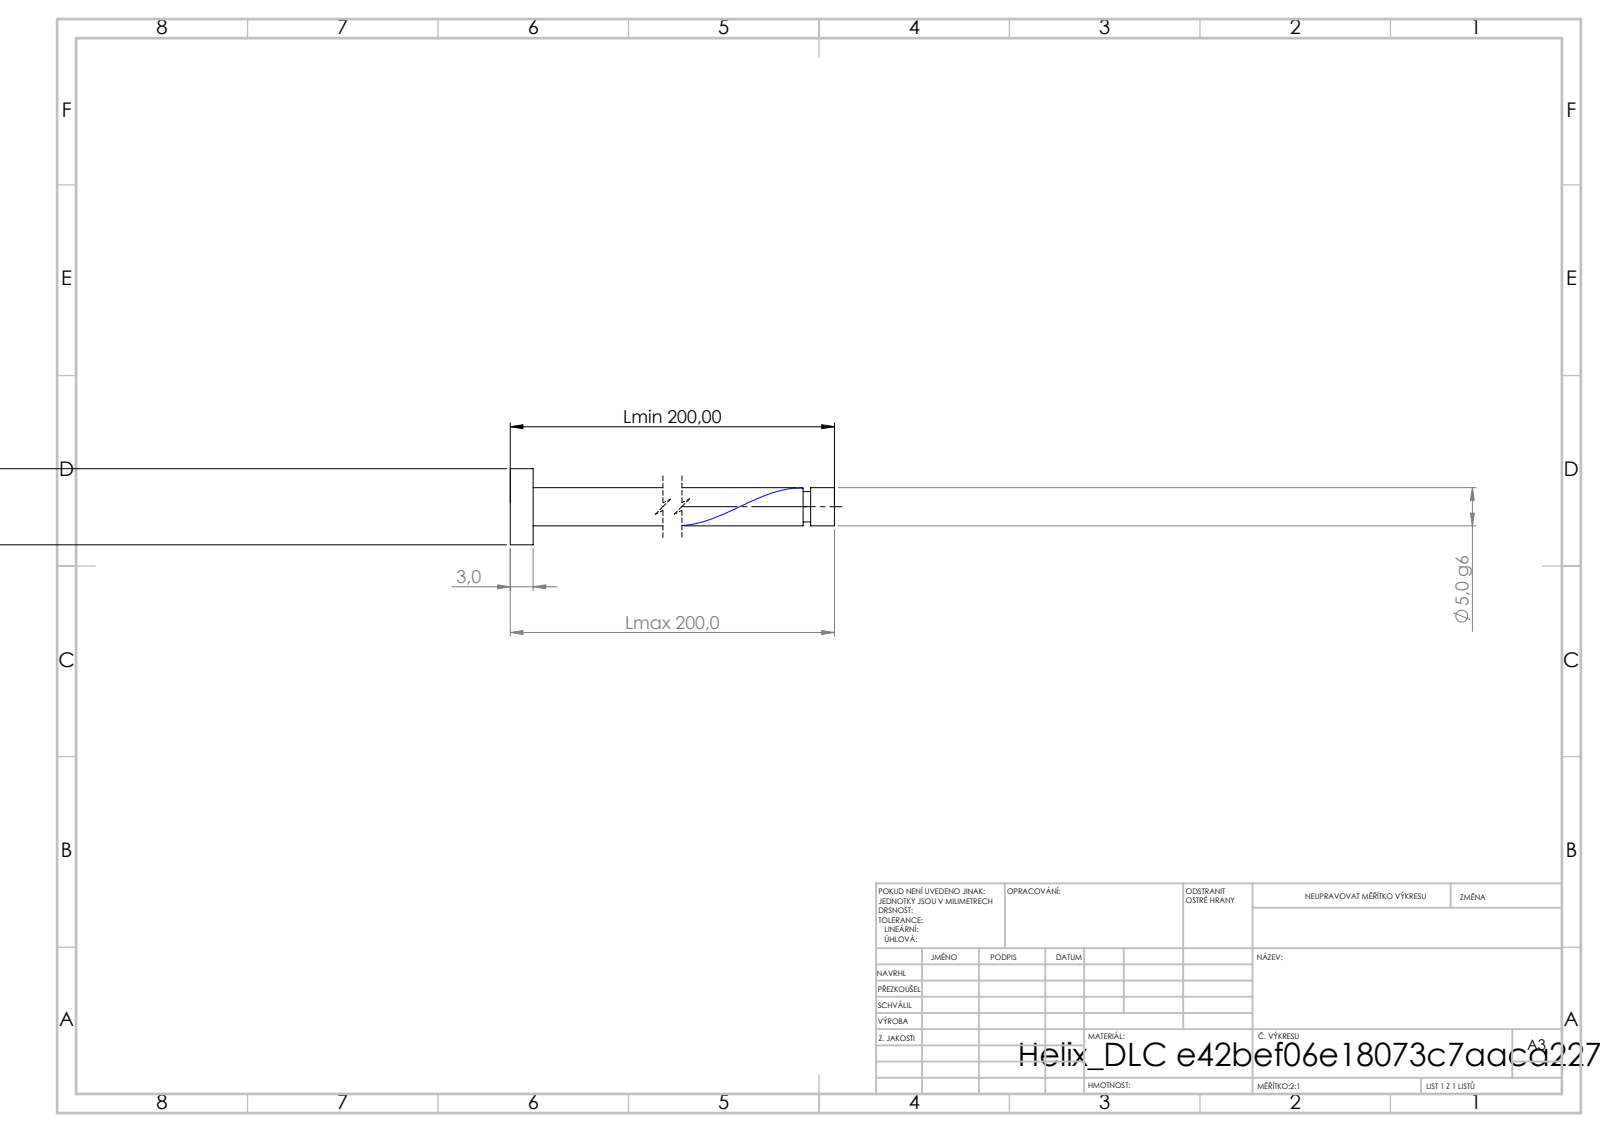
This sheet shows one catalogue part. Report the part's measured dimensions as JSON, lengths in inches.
{"step_written_by": "SolidWorks 2019 (CONFIG_CONTROL_DESIGN)", "units": "inches", "bodies": {"solids": 1, "faces": 21, "planar": 6, "cylindrical": 14, "other": 1}, "overall_size": [7.874, 0.394, 0.394], "volume_in3": 0.248, "surface_area_in2": 5.287, "round_bosses_or_shafts": [[0.394, 1], [0.197, 1], [0.157, 1]], "face_to_face_distances": [0.118, 7.874, 7.756, 7.751, 7.633, 0.123, 7.712, 7.594, 0.039, 0.162]}
